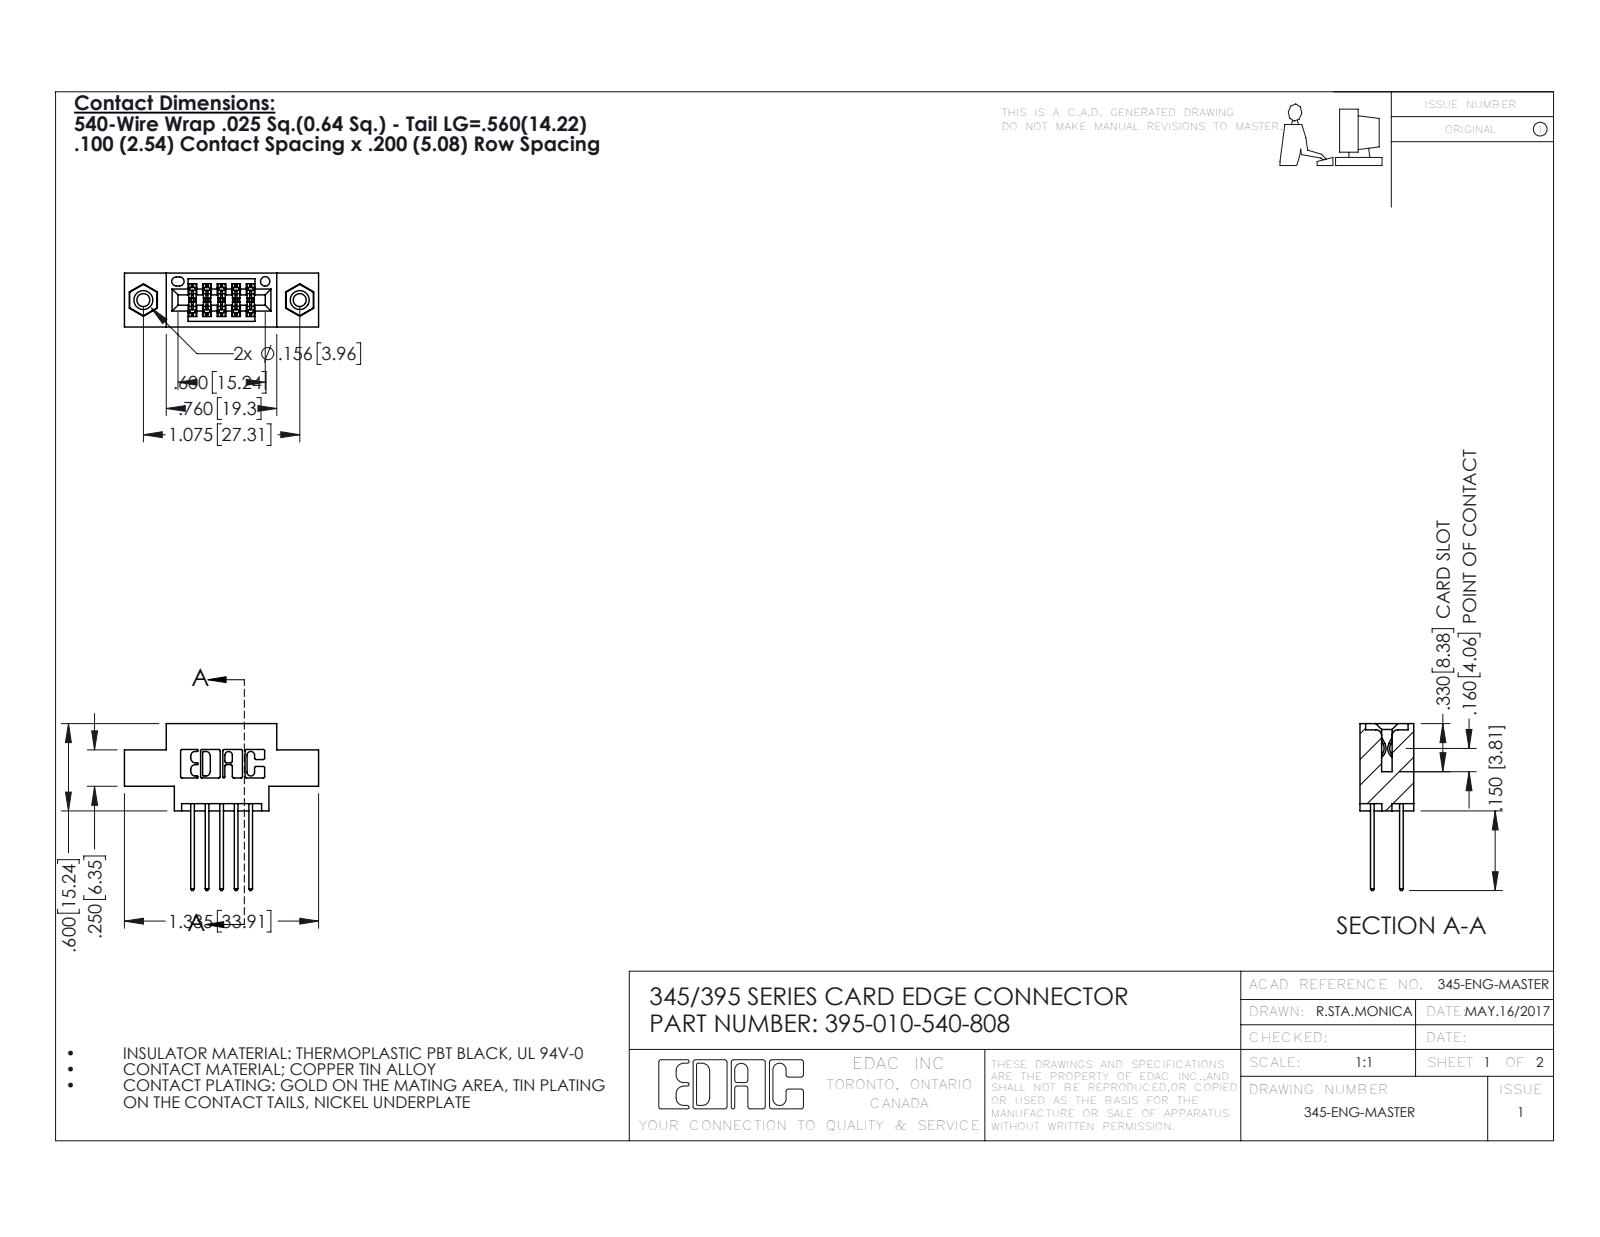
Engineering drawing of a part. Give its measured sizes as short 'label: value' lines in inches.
name: 345-292-001_345-293-140; 345-250-001_345-250-003-102; 345 Part_0.170 Offset - 0.156 Dia-TI; 395-010-540-808
written by: SolidWorks 2016 (CONFIG_CONTROL_DESIGN)
unit: in
bodies: 13 solids, 690 faces (446 planar, 228 cylindrical, 16 other)
size: 1.335 × 1.147 × 0.37
volume: 0.175 in³; area: 5.977 in²
holes: 2× ⌀0.089, 2× ⌀0.125, 2× ⌀0.156, 1× ⌀0.064
bosses: 2× ⌀0.155
rounds: 22× R0.01, 15× R0.006, 10× R0.01, 6× R0.007, 6× R0.031, 3× R0.026, 2× R0.014, 2× R0.019
face distances: 0.2, 0.37, 0.072, 0.298, 0.1, 0.098, 0.272, 0.025, 0.225, 0.25
hole spacings: 0.27, 0.847, 1.075
